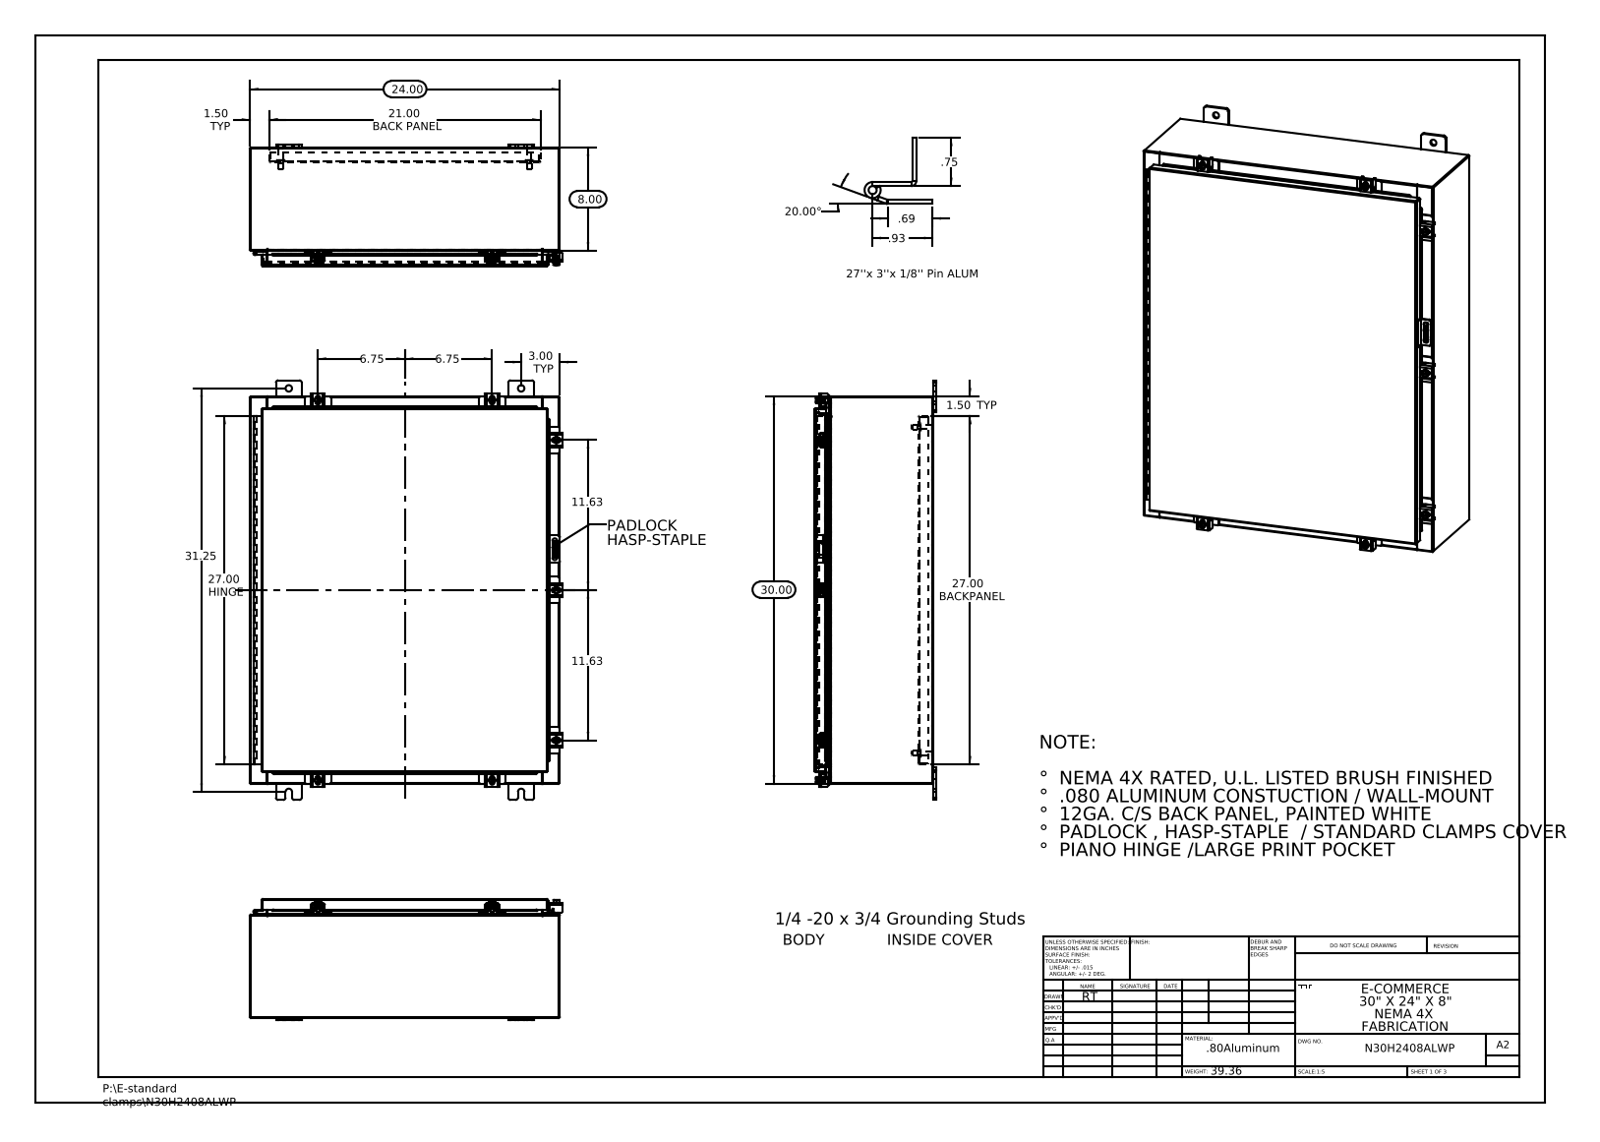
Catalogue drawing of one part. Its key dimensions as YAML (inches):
part_name: "N30H2408ALWP Mounting Feet; N30H2408ALWP Padlock Staple; N30H2408ALWP Bottom; N30H2408ALWP Cover (+8 more)"
step_written_by: "SolidWorks 2013 (CONFIG_CONTROL_DESIGN)"
units: inches
bodies: {solids: 52, faces: 1990, planar: 1056, cylindrical: 830, other: 104}
overall_size: [32.5, 24.211, 9.389]
volume: 264.8
surface_area: 6618
round_holes:
  - {diameter: 0.5, count: 8}
  - {diameter: 0.213, count: 7}
  - {diameter: 0.26, count: 7}
  - {diameter: 0.125, count: 2}
  - {diameter: 0.125, count: 1}
round_bosses_or_shafts:
  - {diameter: 0.25, count: 8}
  - {diameter: 0.5, count: 7}
  - {diameter: 0.399, count: 7}
  - {diameter: 0.625, count: 4}
  - {diameter: 0.375, count: 4}
  - {diameter: 0.33, count: 4}
partial_cylinders:
  - {radius: 0.06, count: 34}
  - {radius: 0.013, count: 27}
  - {radius: 0.19, count: 24}
  - {radius: 0.088, count: 21}
  - {radius: 0.12, count: 14}
  - {radius: 0.141, count: 14}
  - {radius: 0.05, count: 11}
  - {radius: 0.08, count: 10}
face_to_face_distances: [0.075, 9.126, 9.201, 9.051, 0.104, 1, 1.075, 8.051, 8.126, 1.179]
hole_center_spacings: [27.501, 31.878, 1.858, 2.277, 2.326, 2.423, 3.561, 3.561]
